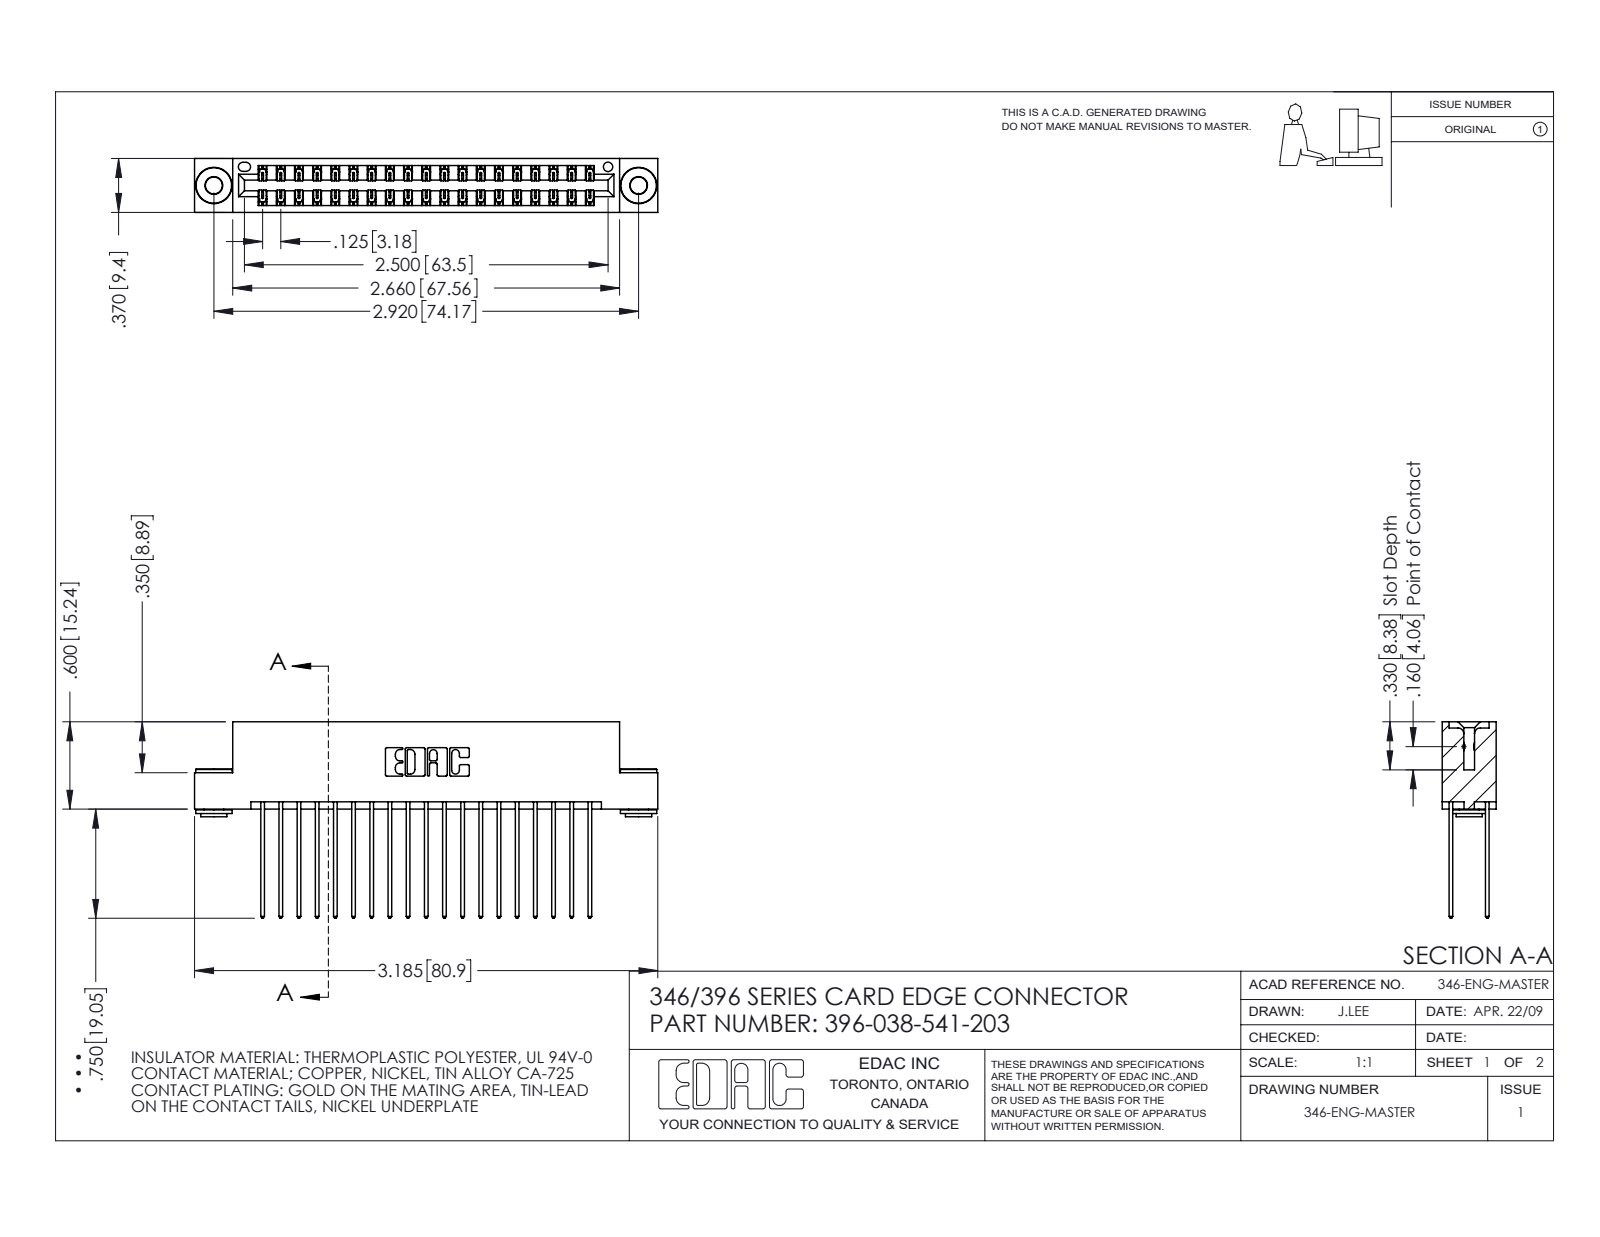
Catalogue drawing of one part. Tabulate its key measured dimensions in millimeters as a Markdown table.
| quantity | value |
| --- | --- |
| part name | 345-292-001_345-293-141; 396-038-541-203; 346 Part_Flush Mounting Lugs - 0.156 Dia-TH; 345-250-002_345-250-002-102 |
| STEP written by | SolidWorks 2016 (CONFIG_CONTROL_DESIGN) |
| units | millimeters |
| bodies | 41 solids, 2136 faces (1416 planar, 712 cylindrical, 8 other) |
| overall size | 80.9 × 34.3 × 9.4 |
| volume | 7 950 mm³ |
| surface area | 11 820 mm² |
| round holes (diameter × count) | 2.9 × 2, 4 × 2, 1.6 × 1 |
| round bosses / shafts (diameter × count) | 6.4 × 2, 4.6 × 2, 3.5 × 2 |
| partial cylindrical surfaces (radius × count) | 0.2 × 57, 0.3 × 38, 0.3 × 22, 0.2 × 6, 0.8 × 6, 0.7 × 3, 0.4 × 2, 0.6 × 2 |
| main face-to-face distances | 1.2, 8.2, 6.4, 0.6, 1.8, 7.6, 9.4, 7, 5.7, 3.8 |
| hole center spacings | 6.2, 68.9, 74.2 |
